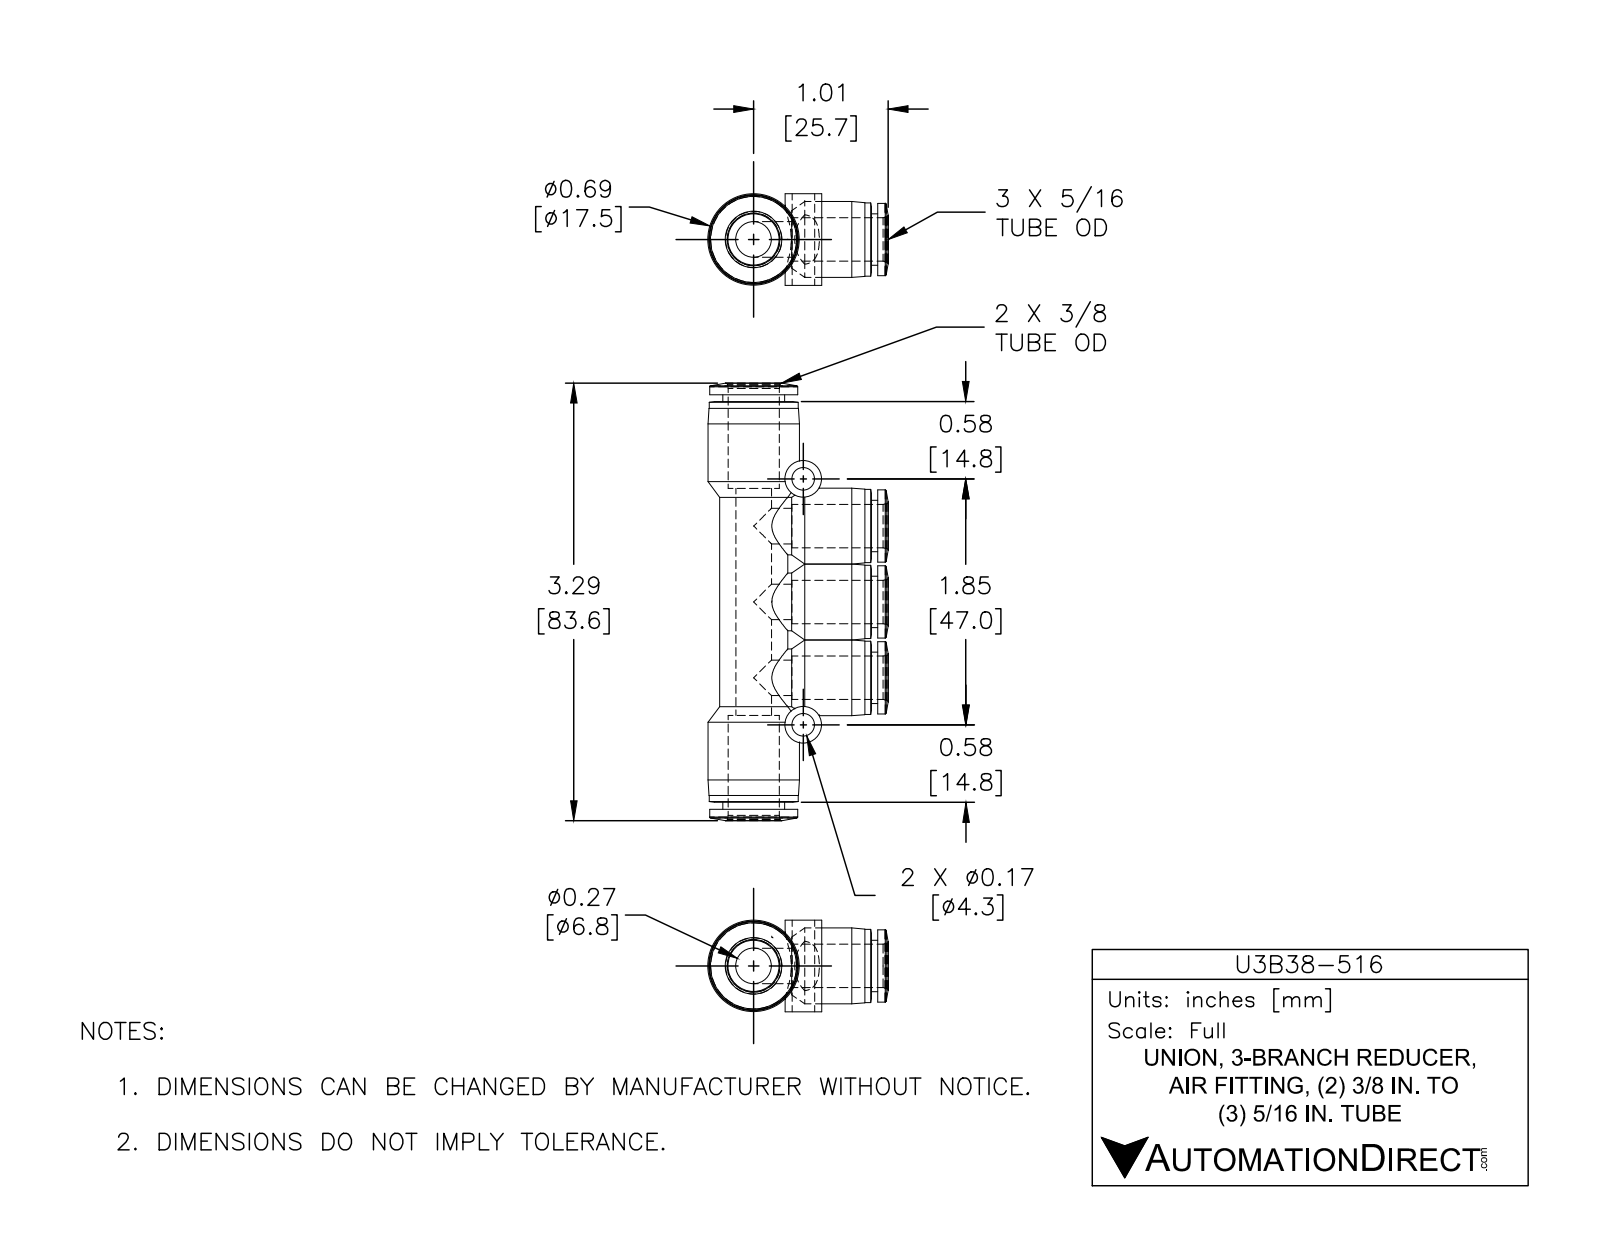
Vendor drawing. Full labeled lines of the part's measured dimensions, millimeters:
Part name (STEP PRODUCT): U3B38-516
STEP written by: SolidWorks 2015 (CONFIG_CONTROL_DESIGN)
Units: millimetres
Bodies: 1 solid, 168 faces (24 planar, 74 cylindrical, 70 other)
Overall size (bounding box): 83.6 × 34.4 × 17.5
Volume: 16 100 mm³ · Surface area: 12 510 mm²
Round holes (diameter × count): ⌀6.8 ×4, ⌀8.3 ×3, ⌀4.3 ×2, ⌀9.8 ×1
Round bosses / shafts (diameter × count): ⌀14.5 ×3, ⌀14 ×3, ⌀13.8 ×3, ⌀11 ×3, ⌀9.8 ×3, ⌀7 ×2, ⌀17.5 ×1, ⌀17 ×1
Main face-to-face distances: 1.2, 1.3, 77.9, 79.2, 17.9, 61.3, 16.6, 60, 76.6, 15.2
Hole centre spacings: 14.5, 29, 47
